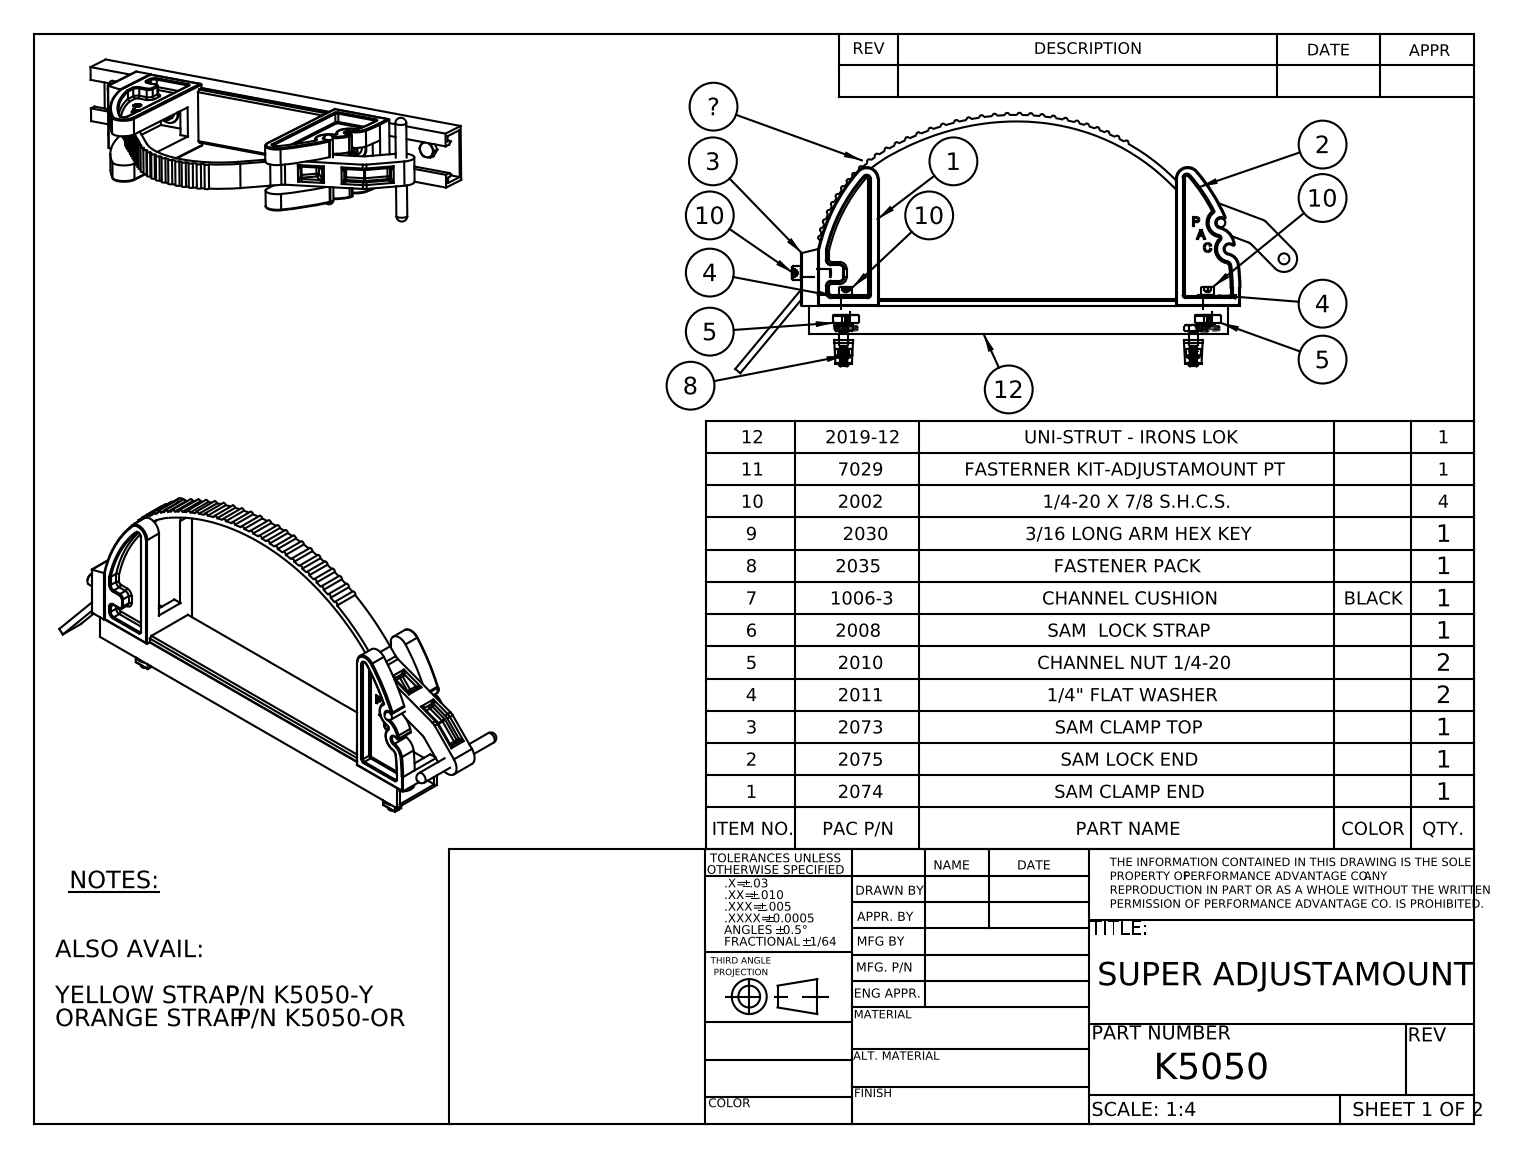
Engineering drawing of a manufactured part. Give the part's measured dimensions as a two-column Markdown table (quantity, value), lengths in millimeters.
| quantity | value |
| --- | --- |
| part name | 7029; 7016; 2049; 2008 - IN USE SAM with nozzle_IN USE FLARES (+8 more) |
| STEP written by | SolidWorks 2014 (CONFIG_CONTROL_DESIGN) |
| units | millimeters |
| bodies | 26 solids, 1430 faces (467 planar, 405 cylindrical, 558 other) |
| overall size | 304.8 × 168.9 × 78.9 |
| volume | 353 500 mm³ |
| surface area | 181 700 mm² |
| round holes (diameter × count) | 5.1 × 6, 6.4 × 2, 6.8 × 2, 6.8 × 2, 7.3 × 2, 8 × 2 |
| round bosses / shafts (diameter × count) | 6.4 × 5, 9.5 × 4, 15.9 × 2, 10.3 × 2, 9.5 × 2, 4.7 × 2, 8 × 1 |
| partial cylindrical surfaces (radius × count) | 1.6 × 49, 0.8 × 32, 1.6 × 23, 1.6 × 12, 0.8 × 8, 1.5 × 8, 3.2 × 7, 2.3 × 6 |
| main face-to-face distances | 31.8, 9.5, 4.8, 20.7, 2, 18.7, 6.8, 2.8, 38.5, 29 |
| hole center spacings | 34.9, 46.1, 46.7, 161.2, 207.3, 207.9, 254 |
